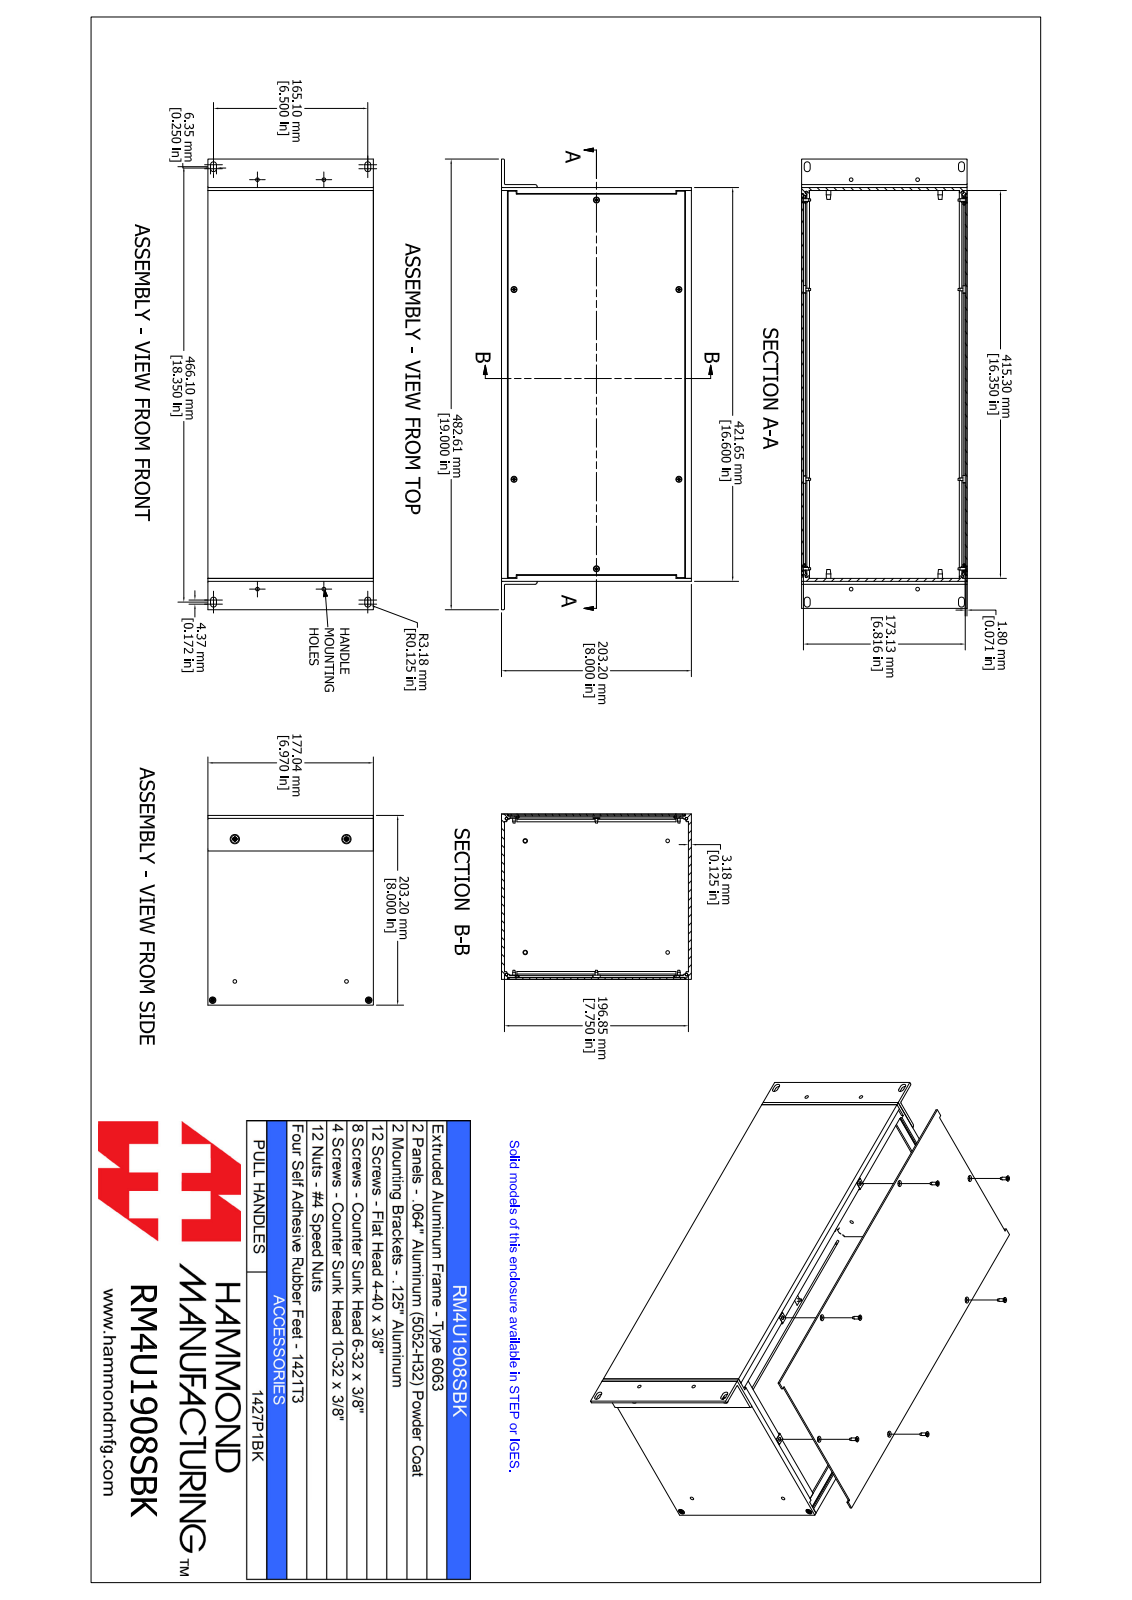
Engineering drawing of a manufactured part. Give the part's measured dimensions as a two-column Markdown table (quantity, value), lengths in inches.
| quantity | value |
| --- | --- |
| part name | RM4U1908SBK |
| STEP written by | SolidWorks 2021 (AUTOMOTIVE_DESIGN) |
| units | inches |
| bodies | 44 solids, 1204 faces (564 planar, 208 cylindrical, 432 other) |
| overall size | 19 × 8 × 6.971 |
| volume | 69.99 in³ |
| surface area | 1 387 in² |
| round holes (diameter × count) | 0.169 × 8, 0.098 × 6, 0.157 × 6, 0.138 × 4, 0.156 × 4, 0.157 × 4, 0.165 × 2, 0.197 × 2 |
| round bosses / shafts (diameter × count) | 0.214 × 6, 0.112 × 6, 0.238 × 4, 0.138 × 4, 0.333 × 2, 0.19 × 2 |
| partial cylindrical surfaces (radius × count) | 0.039 × 18, 0.015 × 16, 0.038 × 16, 0.049 × 12, 0.055 × 8, 0.125 × 8, 0.131 × 8, 0.079 × 2 |
| main face-to-face distances | 0.125, 0.071, 6.887, 7.875, 6.817, 6.958, 8, 16.475, 7.75, 16.6 |
| hole center spacings | 6.854, 1.224, 5.127, 5.128, 5.693, 8.826, 12.274, 12.274 |
